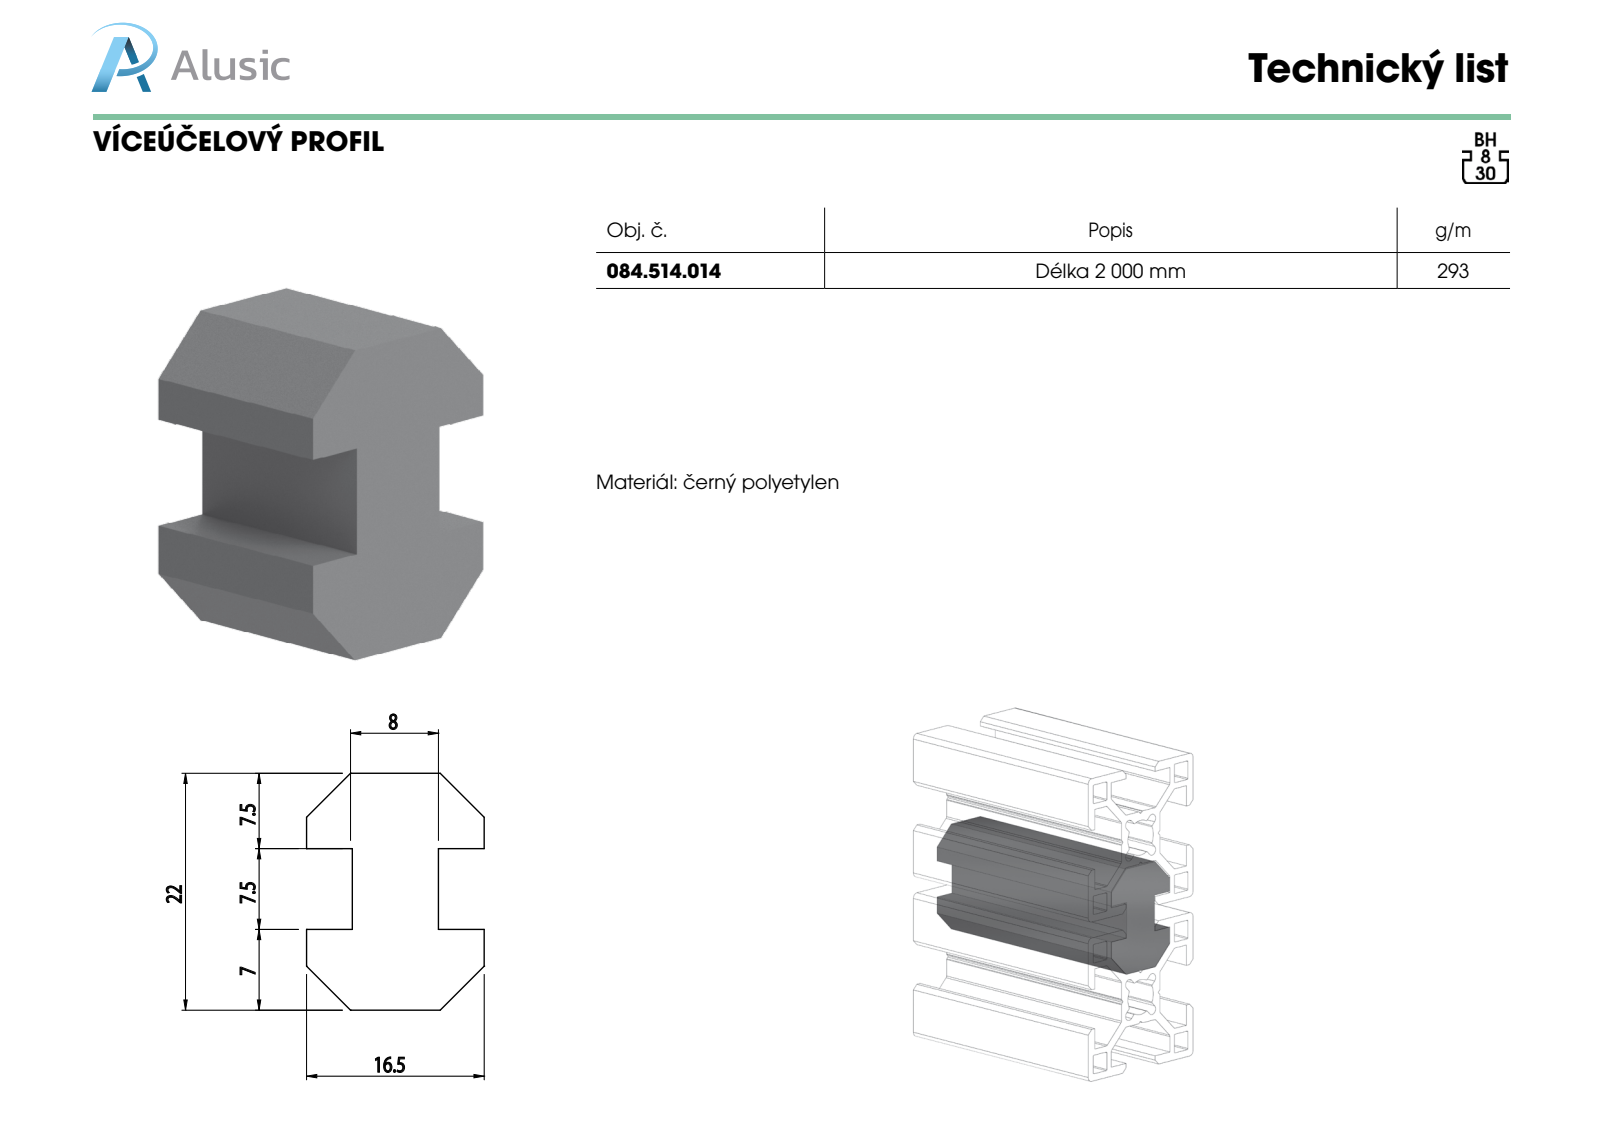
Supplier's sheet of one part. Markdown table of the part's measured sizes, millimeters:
| quantity | value |
| --- | --- |
| part name | 084.514.014 |
| STEP written by | SolidWorks 2012 (CONFIG_CONTROL_DESIGN) |
| units | millimeters |
| bodies | 1 solid, 18 faces (18 planar, 0 cylindrical, 0 other) |
| overall size | 100 × 22 × 16.5 |
| volume | 26 588 mm³ |
| surface area | 8 975 mm² |
| main face-to-face distances | 7.5, 4.25, 12.25, 21.44, 15, 22, 14.5, 7, 8, 16.5 |
